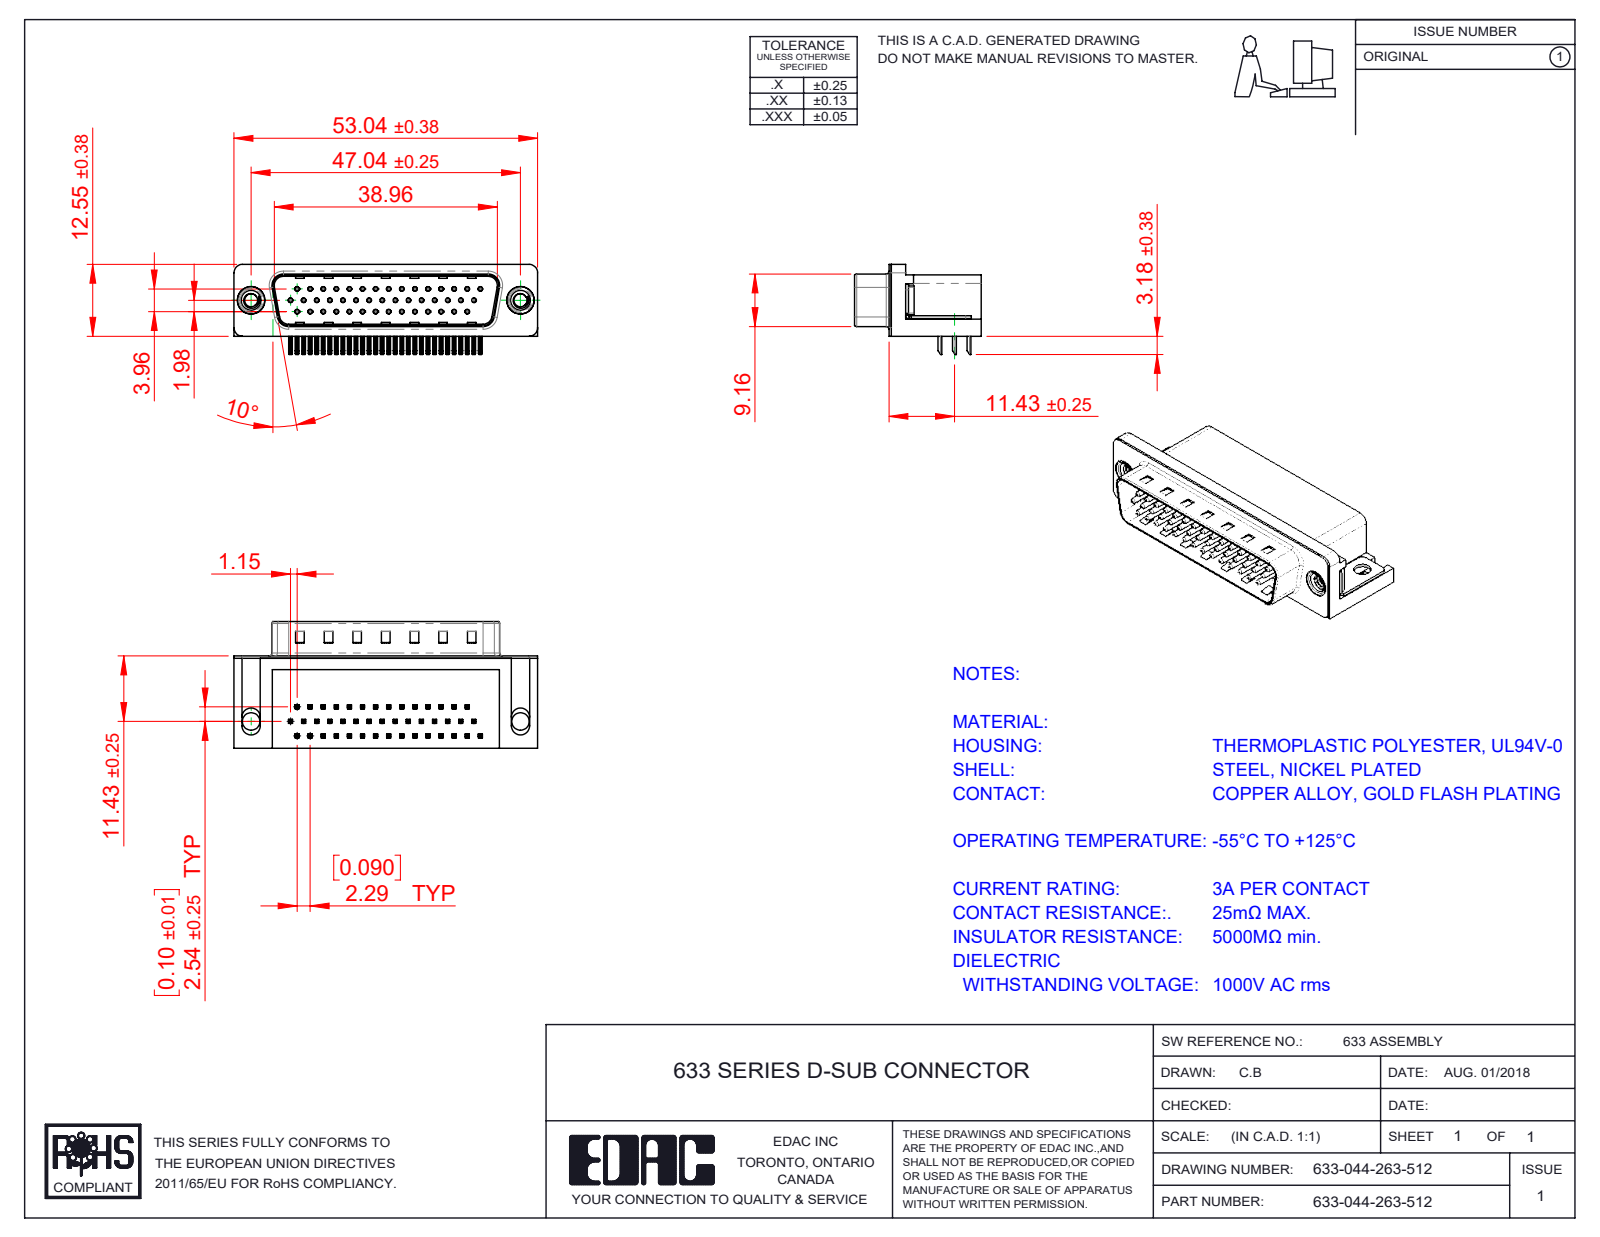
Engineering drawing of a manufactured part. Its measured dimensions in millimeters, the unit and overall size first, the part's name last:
Units: millimetres
Overall size (bounding box): 53.04 × 22.1 × 15.73
Round holes (diameter × count): ⌀0.35 ×44, ⌀0.8 ×44, ⌀2.26 ×2, ⌀3.05 ×2, ⌀4 ×2, ⌀4.8 ×2, ⌀5 ×2
Round bosses / shafts (diameter × count): ⌀0.75 ×44, ⌀4.9 ×2, ⌀4.75 ×2, ⌀3.9 ×2
Partial cylindrical surfaces — rounded edges, fillets, slot ends (radius × count): R0.25 ×184, R0.12 ×88, R1 ×16, R0.5 ×9, R1.6 ×8, R1.5 ×7, R0.9 ×4, R2 ×4
Main face-to-face distances: 0.4, 10.35, 15.7, 2.9, 8.76, 2.5, 2.1, 16.1, 10.7, 2.54
Hole centre spacings: 2.29, 4.57, 4.58, 2.28, 6.87, 9.16, 11.45, 2.27
Volume: 8 114 mm³ · Surface area: 10 206 mm²
Bodies: 50 solids, 3688 faces (2315 planar, 1060 cylindrical, 313 other)
Part name (STEP PRODUCT): 633 Thru Hole Board Mount; 633 4-40 Threaded Rivet; 633 Contact Bottom; 633 Shell_44 Contact (+4 more)
STEP written by: SolidWorks 2016 (CONFIG_CONTROL_DESIGN)
